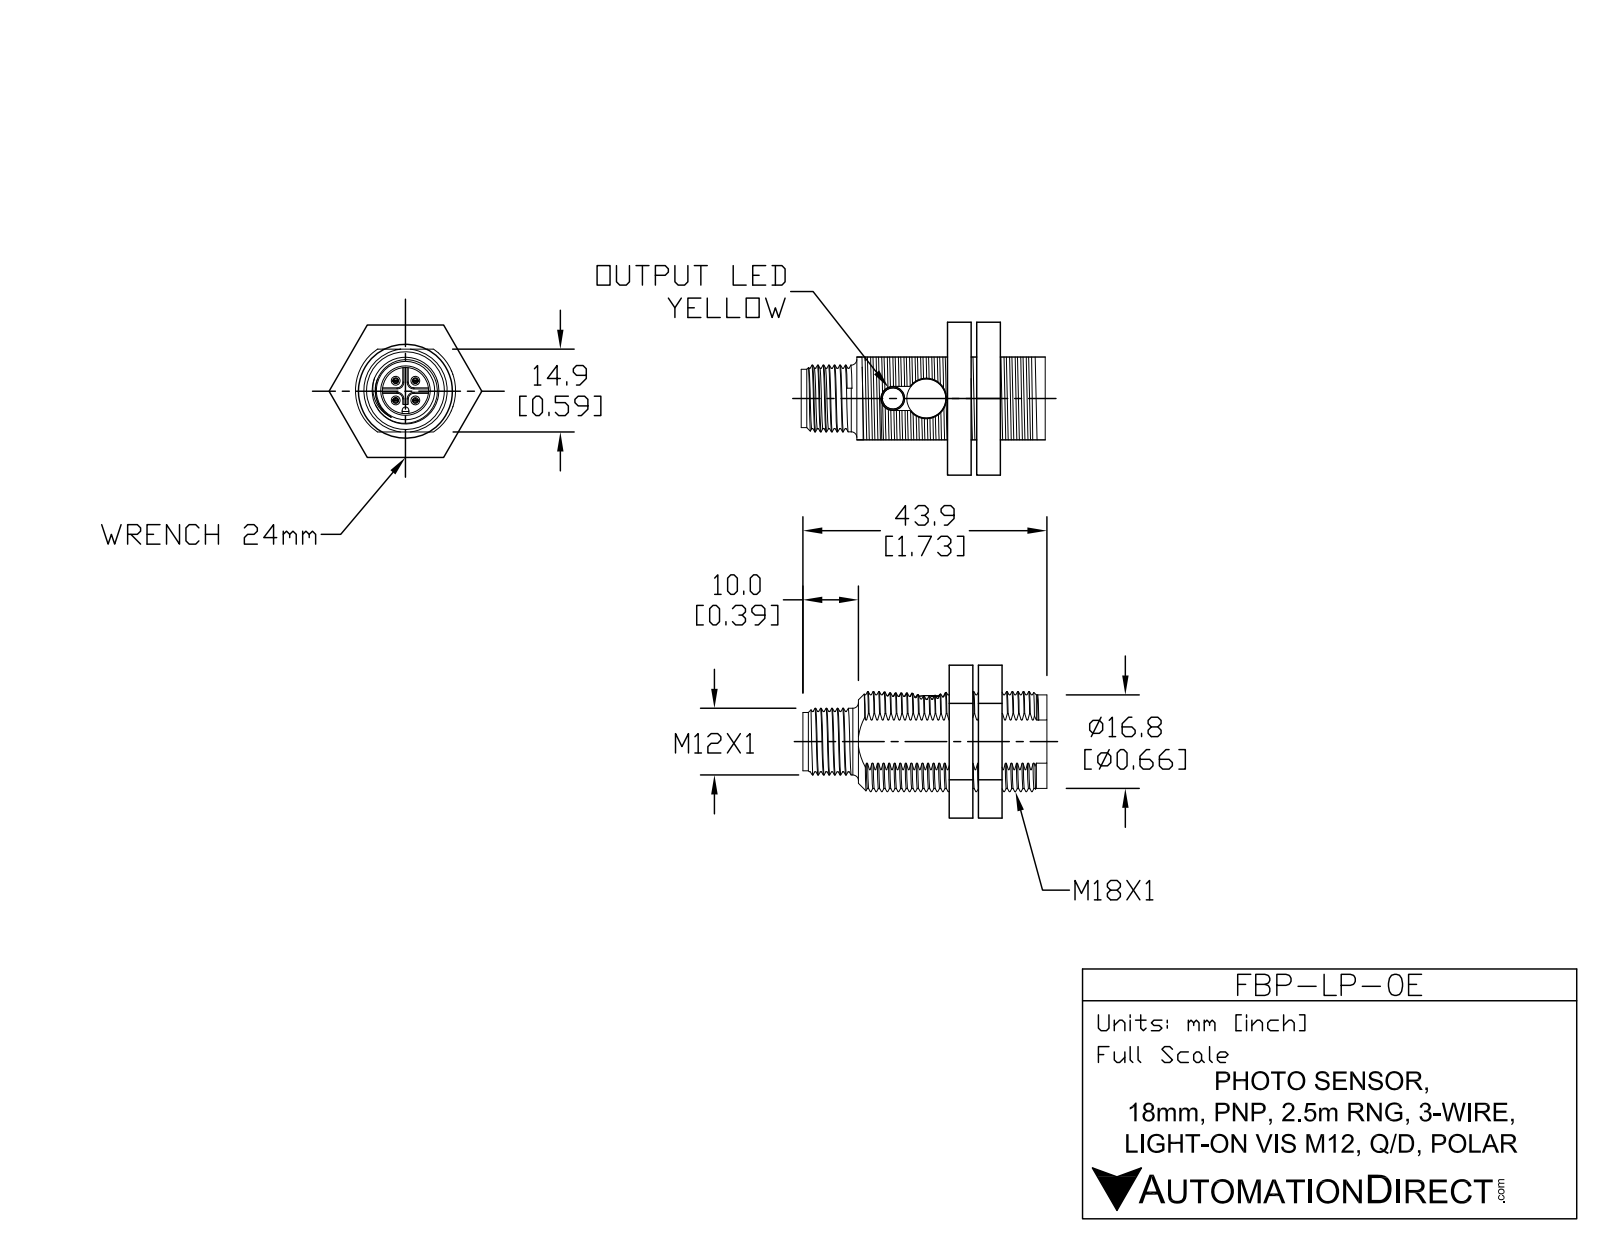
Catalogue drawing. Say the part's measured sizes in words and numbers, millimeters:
The part is named "FBP-LP-0E". Its 3-D file was written by "SolidWorks 2011 (AUTOMOTIVE_DESIGN)". It is 7 solids with 212 faces: 127 planar, 30 cylindrical and 55 other. Overall it measures 43.9 by 27.69 by 24.57 millimeters. Its volume is 10 286 cubic millimeters and its surface area 5 154 square millimeters. Round holes: 1 of diameter 2.36, 1 of diameter 4.26, 1 of diameter 7.25, 1 of diameter 8.4. Round bosses or shafts: 4 of diameter 1, 1 of diameter 12, 1 of diameter 10.4. Partial cylindrical surfaces (rounded edges, fillets, slot ends): 2 of radius 6.46, 2 of radius 7.46, 1 of radius 0.5, 1 of radius 8.4, 1 of radius 8.5, 1 of radius 9. The main face-to-face distances are 8, 4.5, 24, 15, 1, 12.5, 4.9, 3.5, 12.9, 13.9. The hole center spacings are 6.61.
